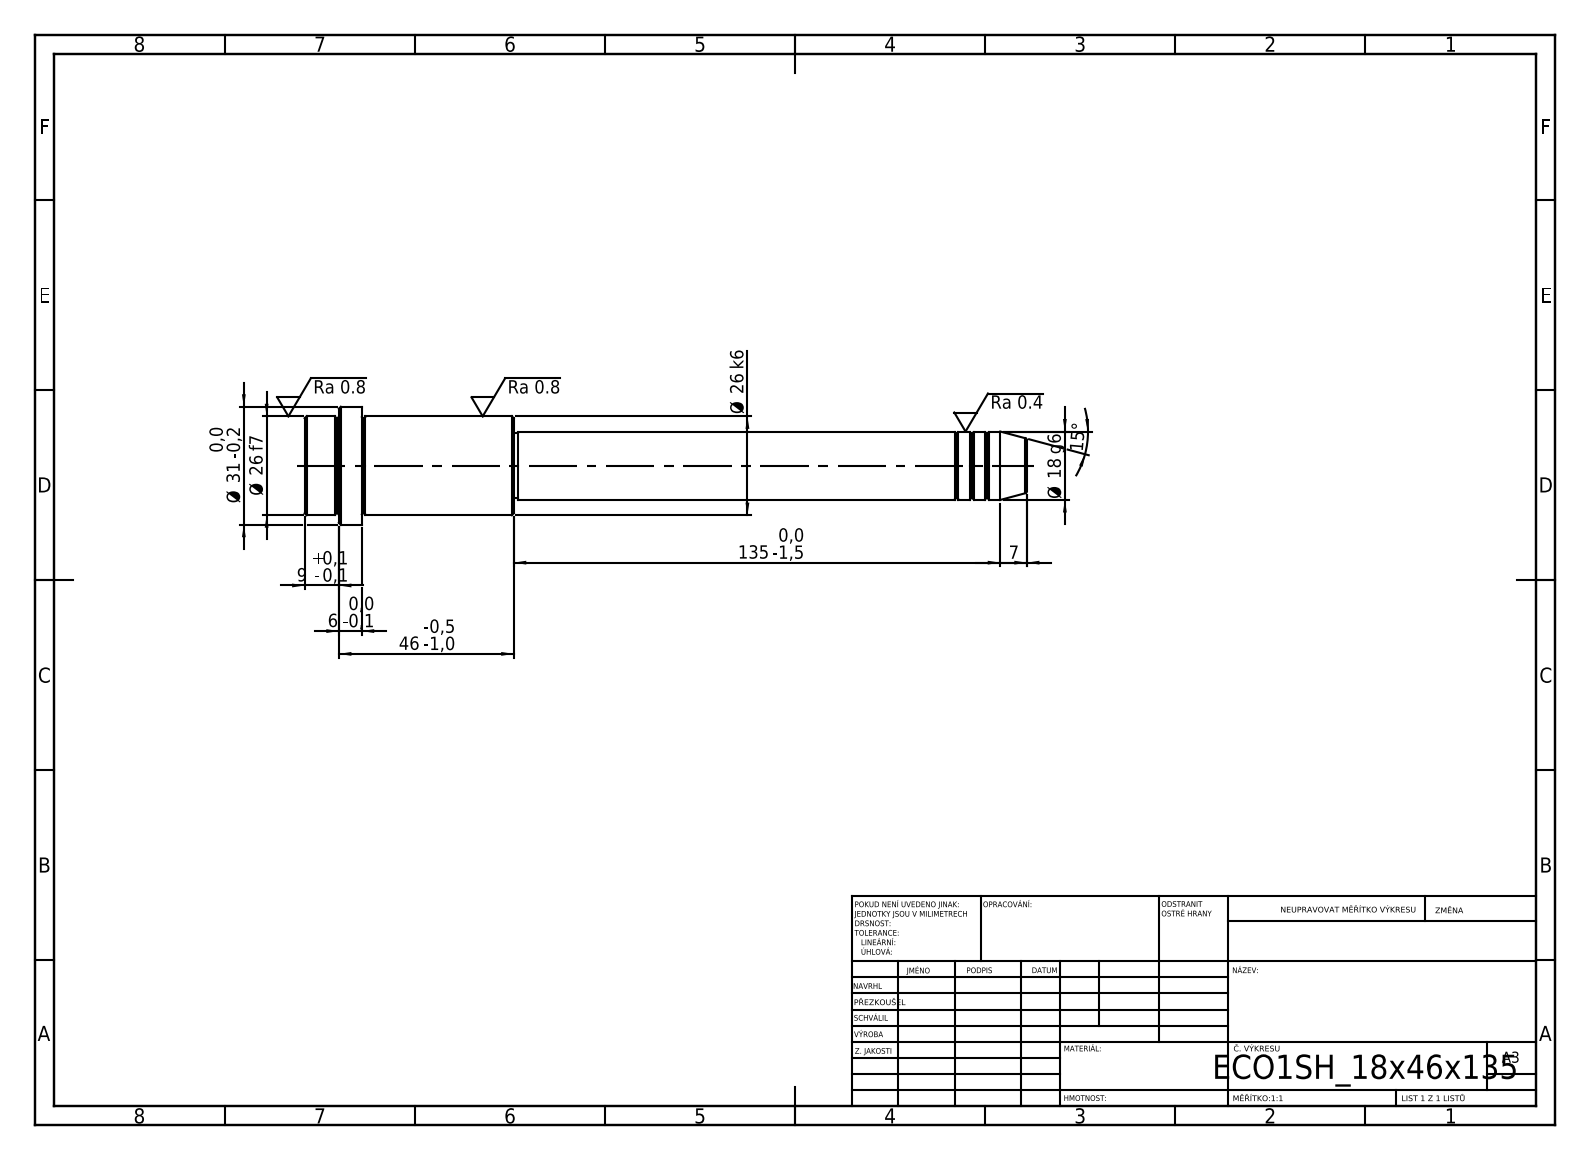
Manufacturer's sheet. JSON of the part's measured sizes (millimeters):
{"step_written_by": "SolidWorks 2019 (CONFIG_CONTROL_DESIGN)", "units": "millimeters", "bodies": {"solids": 1, "faces": 52, "planar": 6, "cylindrical": 16, "other": 30}, "overall_size": [190, 31, 31], "volume_mm3": 64363, "surface_area_mm2": 13750, "round_bosses_or_shafts": [[31, 1], [26, 1], [18, 1], [17, 1]], "face_to_face_distances": [55, 40, 15, 46, 6, 9, 135, 175, 181, 190]}
